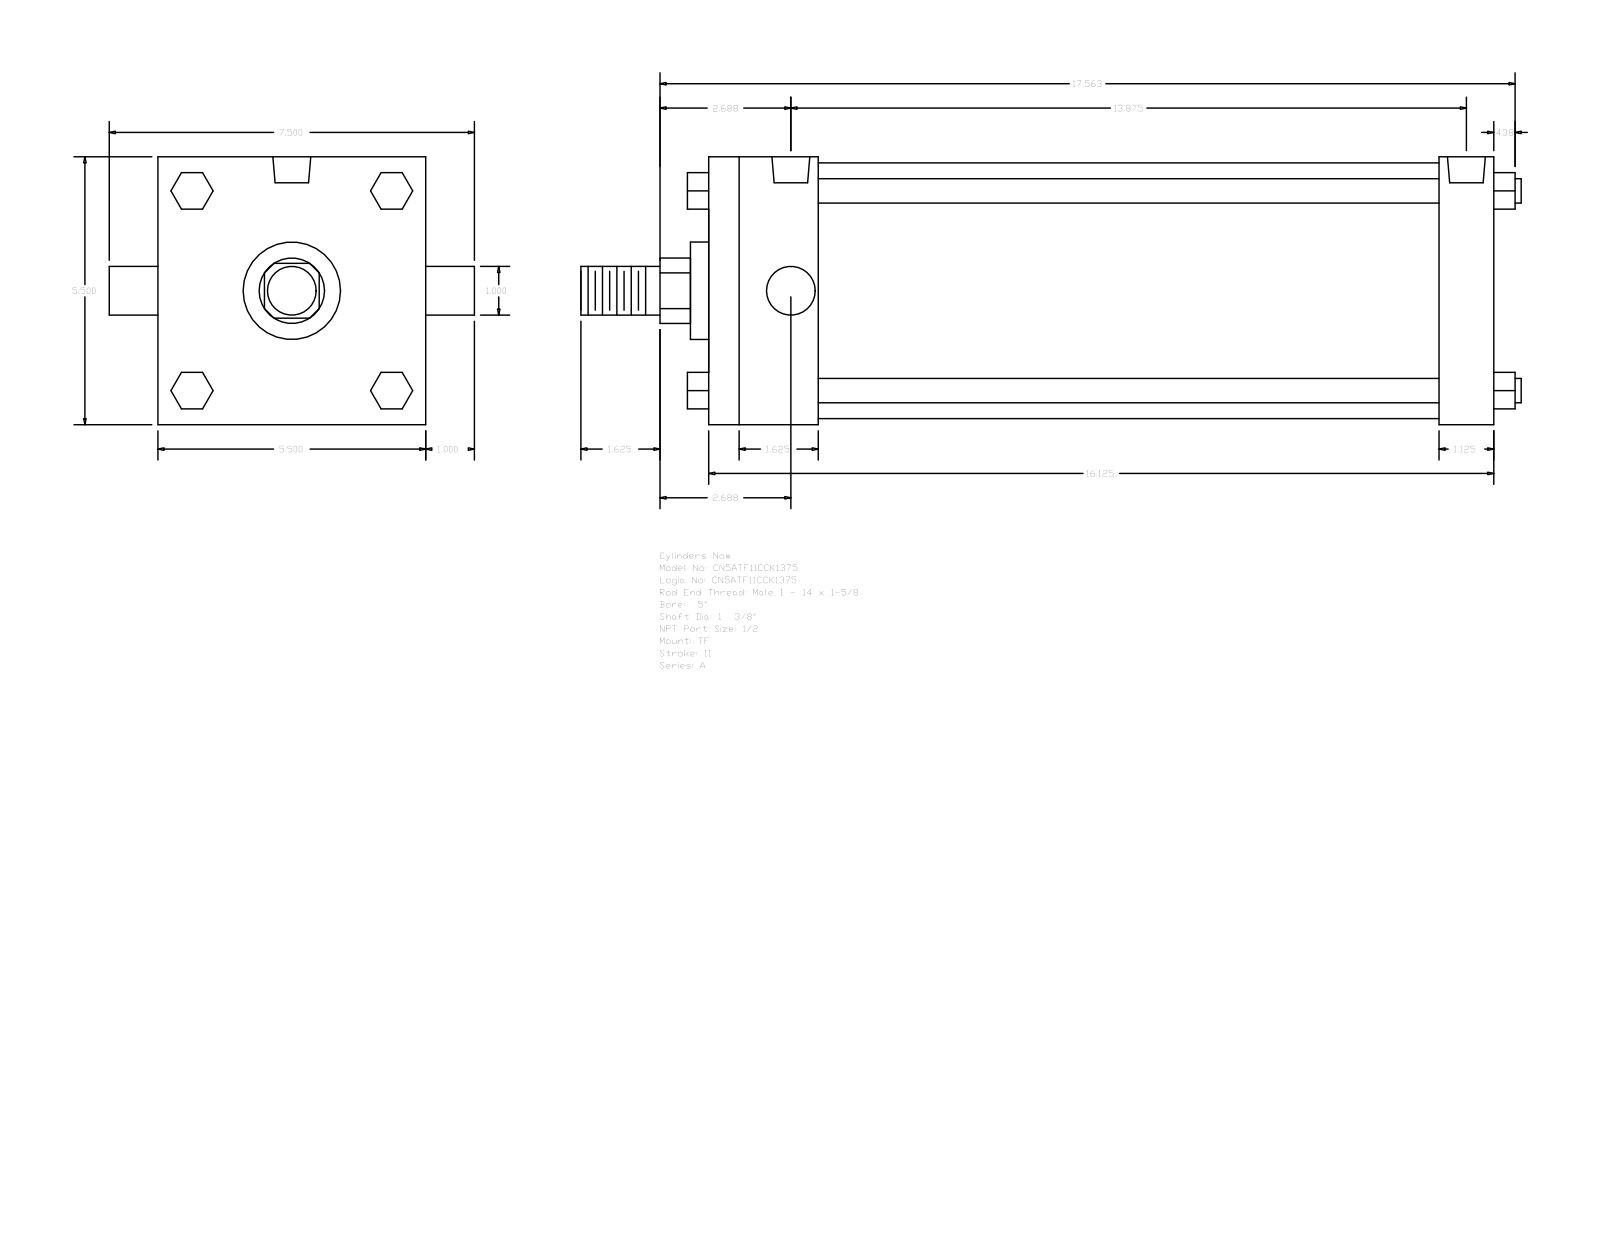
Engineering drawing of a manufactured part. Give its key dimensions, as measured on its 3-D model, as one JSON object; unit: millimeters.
{"part_name": "A_TF__0500_1.375", "step_written_by": "GSSL Pune (CONFIG_CONTROL_DESIGN)", "units": "millimeters", "bodies": {"solids": 0, "faces": 120, "planar": 92, "cylindrical": 28, "other": 0}, "overall_size": [490.54, 190.5, 139.7], "round_holes": [[8.73, 3], [19.77, 2]], "round_bosses_or_shafts": [[12.7, 4], [25.4, 2], [133.35, 1], [50.8, 1], [34.92, 1]], "partial_cylinders_radius": [[17.06, 1]], "face_to_face_distances": [139.7, 409.58, 57.15, 28.58, 381, 323.85, 352.43, 19.05, 52.07, 90.18], "hole_center_spacings": [2.39, 350.04, 347.65, 352.43]}
